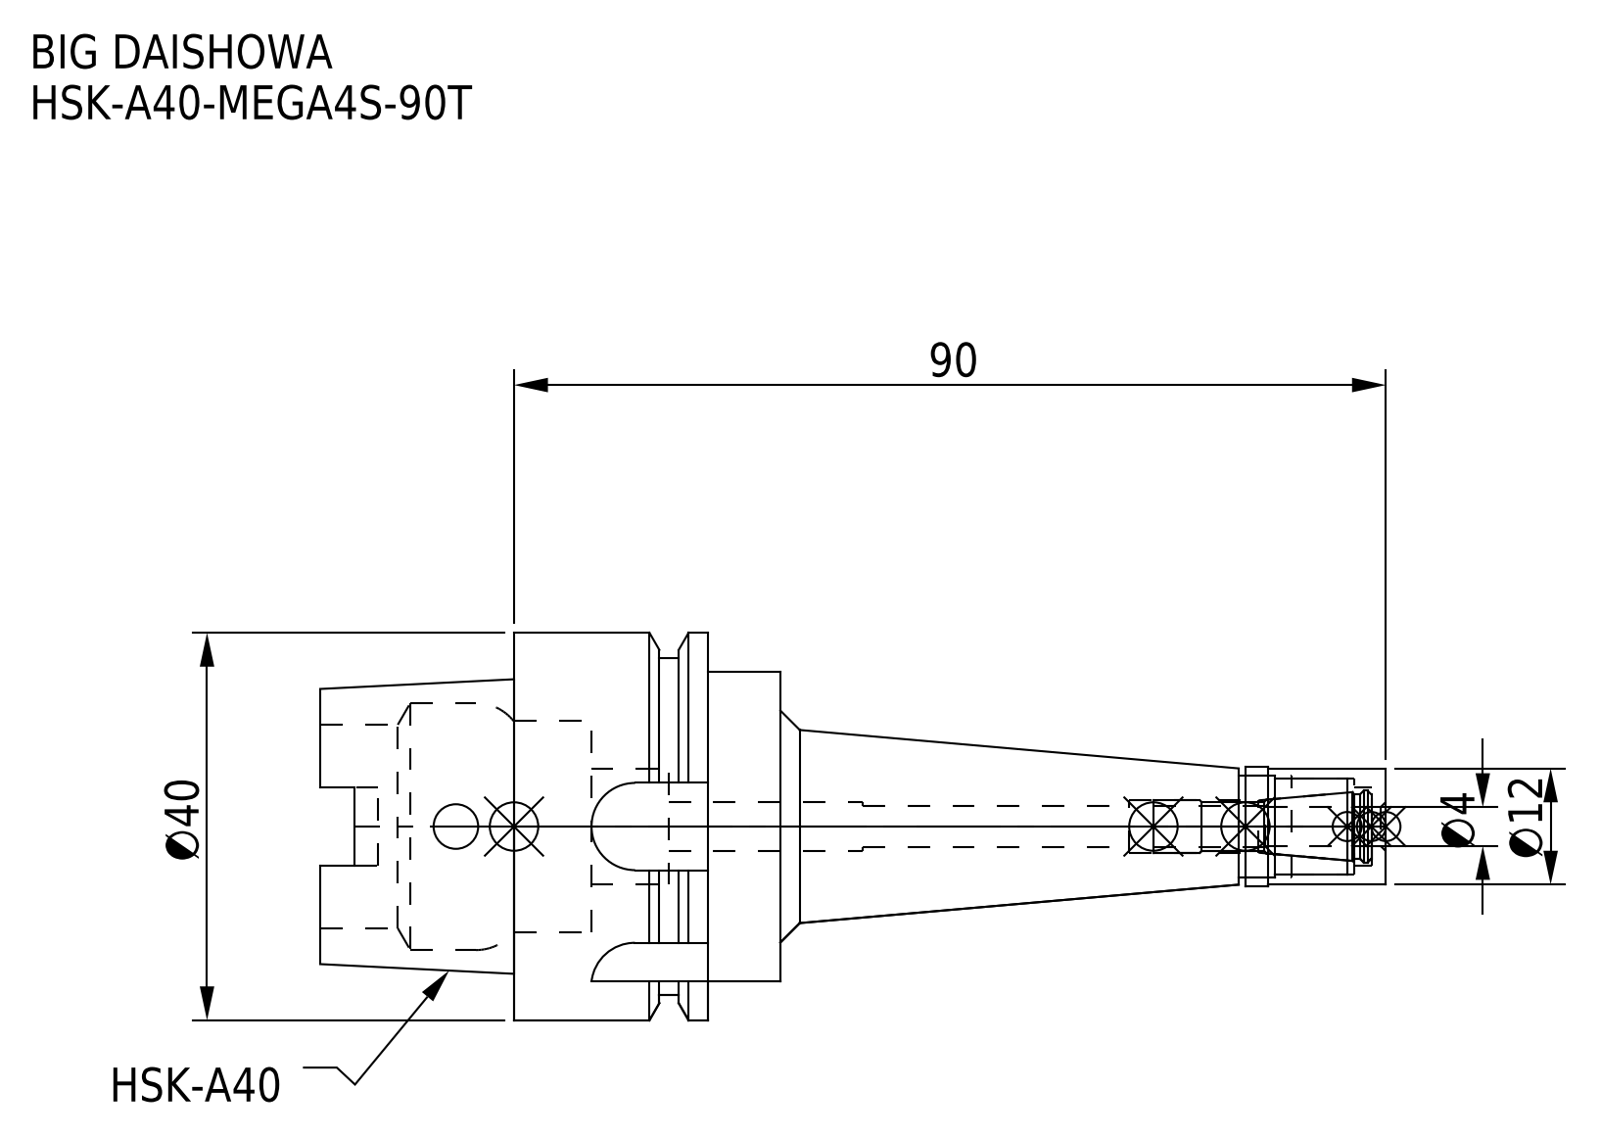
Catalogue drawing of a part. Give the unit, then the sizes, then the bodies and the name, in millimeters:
Units: millimetres
Overall size (bounding box): 110 × 40 × 40
Round holes (diameter × count): ⌀4.1 ×1, ⌀4.2 ×1, ⌀4.6 ×1, ⌀5 ×1, ⌀5.4 ×1, ⌀8 ×1, ⌀10 ×1, ⌀10.5 ×1, ⌀12 ×1, ⌀21 ×1, ⌀21.8 ×1, ⌀25.5 ×1
Round bosses / shafts (diameter × count): ⌀40 ×1, ⌀34.8 ×1, ⌀32 ×1, ⌀12.3 ×1
Partial cylindrical surfaces — rounded edges, fillets, slot ends (radius × count): R1.88 ×4, R4.5 ×4
Main face-to-face distances: 20, 7.5, 27.5, 7.95, 19.55, 12.05, 47.5, 40, 27.95, 34
Volume: 40 643 mm³ · Surface area: 14 982 mm²
Bodies: 2 solids, 123 faces (47 planar, 54 cylindrical, 22 other)
Part name (STEP PRODUCT): HSK-A40-MEGA4S-90T-040.stp; HA40MS04090T-040_ASM.stp; HSK-A40-MEGA4S-90T_1.stp; HSK-A40-MEGA4S-90T-040-FreeParts (+3 more)
STEP written by: SolidWorks 2019 (CONFIG_CONTROL_DESIGN)
